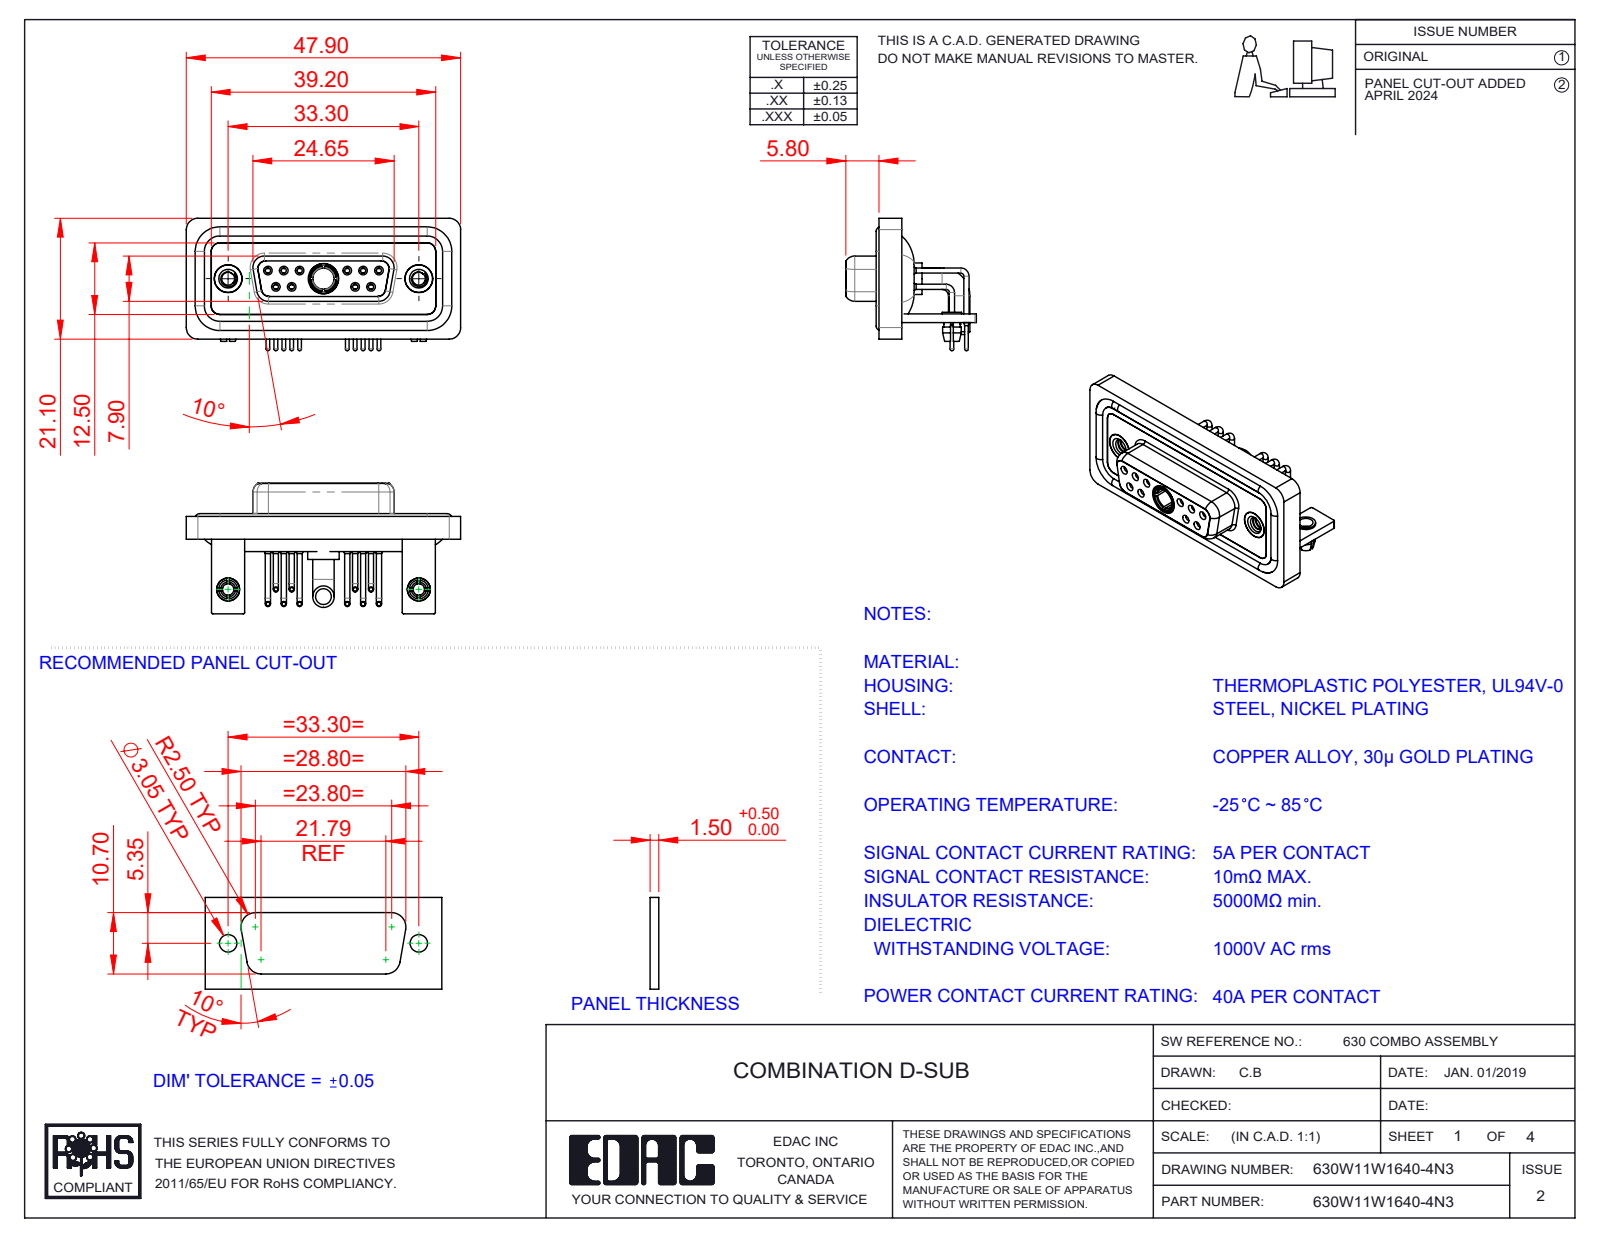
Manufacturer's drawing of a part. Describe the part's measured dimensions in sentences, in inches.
The part is named "630Combo Board Lock_50 Contacts; 630Combo Contact Row 1_50 Contacts; 630W11W1640-4N3; 630Combo Waterproof Housing_15 Contacts (+7 more)". Its 3-D file was written by "SolidWorks 2023 (CONFIG_CONTROL_DESIGN)". It is 23 solids with 1134 faces: 352 planar, 499 cylindrical and 283 other. Overall it measures 1.886 by 0.91 by 0.898 inches. Its volume is 0.408 cubic inches and its surface area 17.76 square inches. Round holes: 12 of diameter 0.079, 10 of diameter 0.035, 10 of diameter 0.043, 10 of diameter 0.059, 6 of diameter 0.067, 4 of diameter 0.063, 3 of diameter 0.191, 2 of diameter 0.089, 2 of diameter 0.098, 2 of diameter 0.126, 2 of diameter 0.157, 2 of diameter 0.159. Round bosses or shafts: 10 of diameter 0.063, 10 of diameter 0.035, 10 of diameter 0.026, 2 of diameter 0.195, 2 of diameter 0.189, 2 of diameter 0.157, 2 of diameter 0.148, 2 of diameter 0.134. Partial cylindrical surfaces (rounded edges, fillets, slot ends): 21 of radius 0.079, 18 of radius 0.059, 16 of radius 0.01, 12 of radius 0.053, 8 of radius 0.063, 5 of radius 0.02, 4 of radius 0.024, 4 of radius 0.026. The main face-to-face distances are 0.016, 0.114, 0.059, 0.071, 0.146, 0.043, 0.063, 0.161, 0.031, 0.098. The hole center spacings are 0.124, 0.109, 0.545, 0.436, 0.654, 0.198, 0.198, 0.218.
